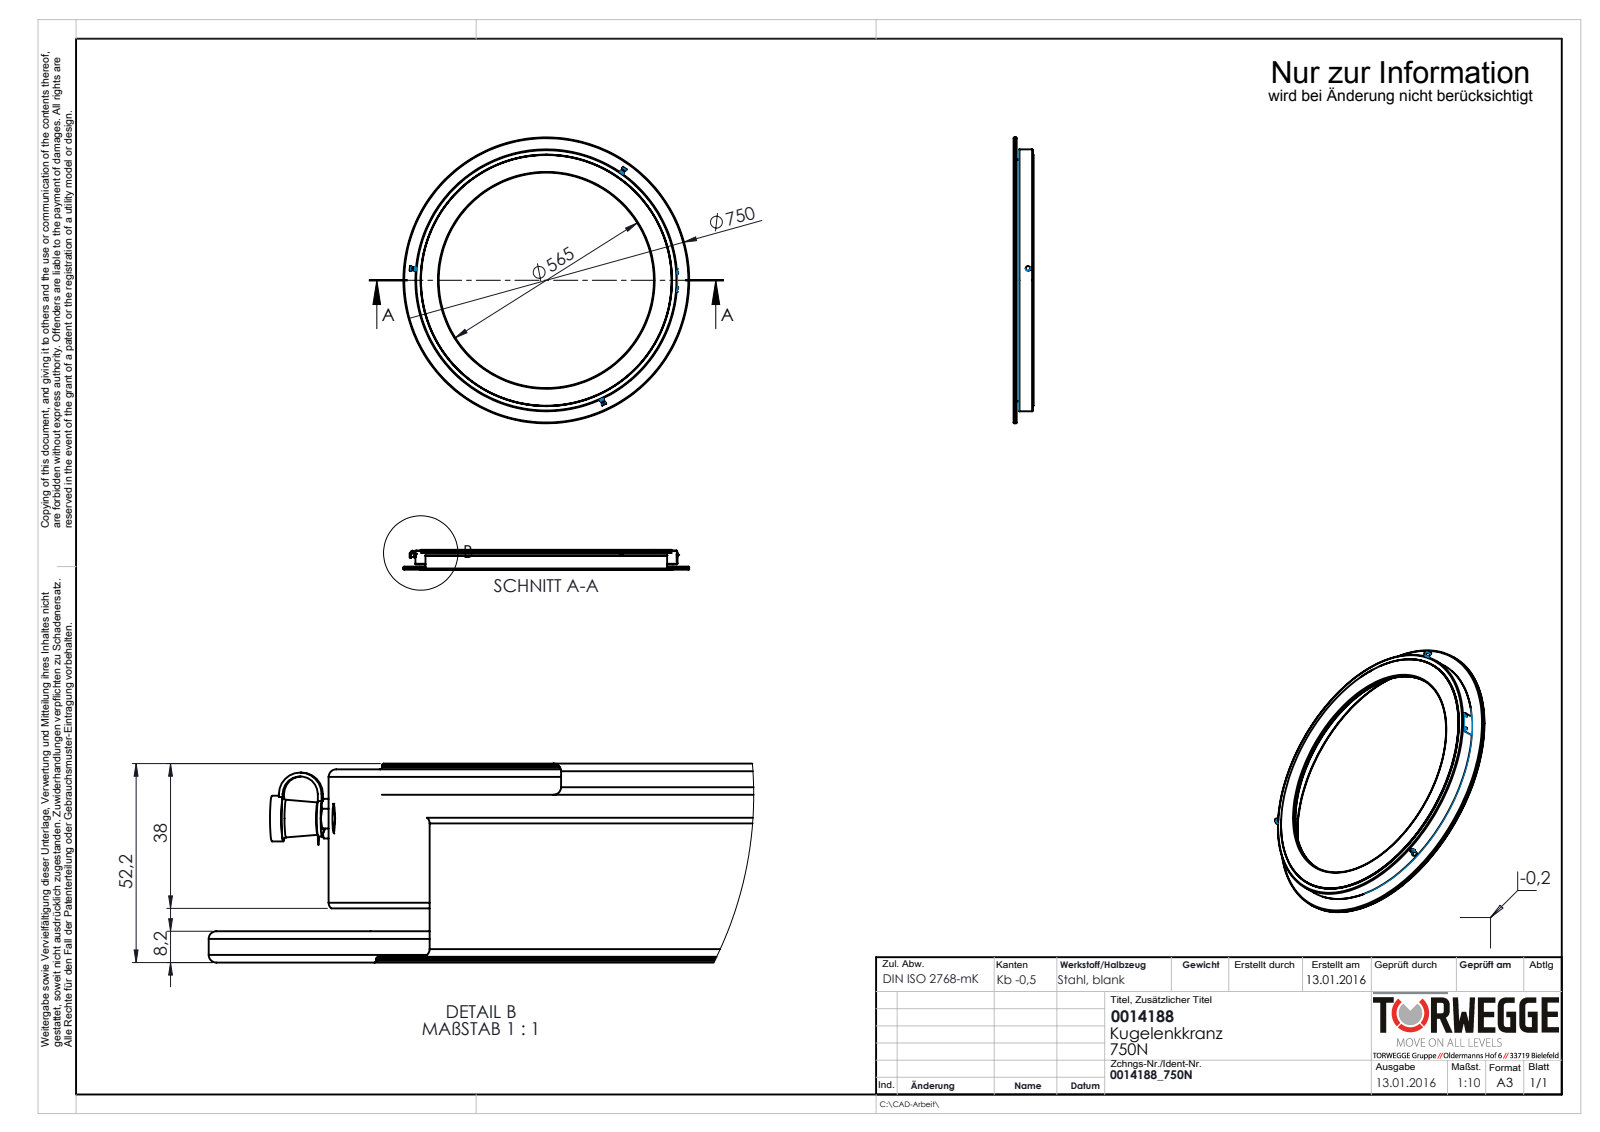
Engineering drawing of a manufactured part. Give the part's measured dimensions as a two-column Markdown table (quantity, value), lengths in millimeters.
| quantity | value |
| --- | --- |
| part name | DK-751_V03; 000012003; NT-0004300; KLK-1300-039_AF0 (+3 more) |
| STEP written by | SolidWorks 2010 (AUTOMOTIVE_DESIGN) |
| units | millimeters |
| bodies | 11 solids, 337 faces (81 planar, 108 cylindrical, 148 other) |
| overall size | 750 × 750 × 52.2 |
| volume | 3 141 000 mm³ |
| surface area | 819 745 mm² |
| round holes (diameter × count) | 1.5 × 5, 6 × 5, 4 × 3, 7.5 × 3, 4.9 × 2, 5.5 × 2, 16.5 × 1, 565 × 1, 634 × 1, 662 × 1 |
| round bosses / shafts (diameter × count) | 12 × 3, 7.5 × 2, 4.9 × 2, 4.7 × 2, 750 × 1, 687 × 1, 659 × 1, 16.1 × 1 |
| partial cylindrical surfaces (radius × count) | 5 × 7, 1.75 × 3, 4.62 × 3, 5.62 × 3, 344.25 × 1 |
| main face-to-face distances | 8.2, 44, 35.8, 52.2, 1.5, 50.7, 6.7, 42.5, 14.2, 38 |
